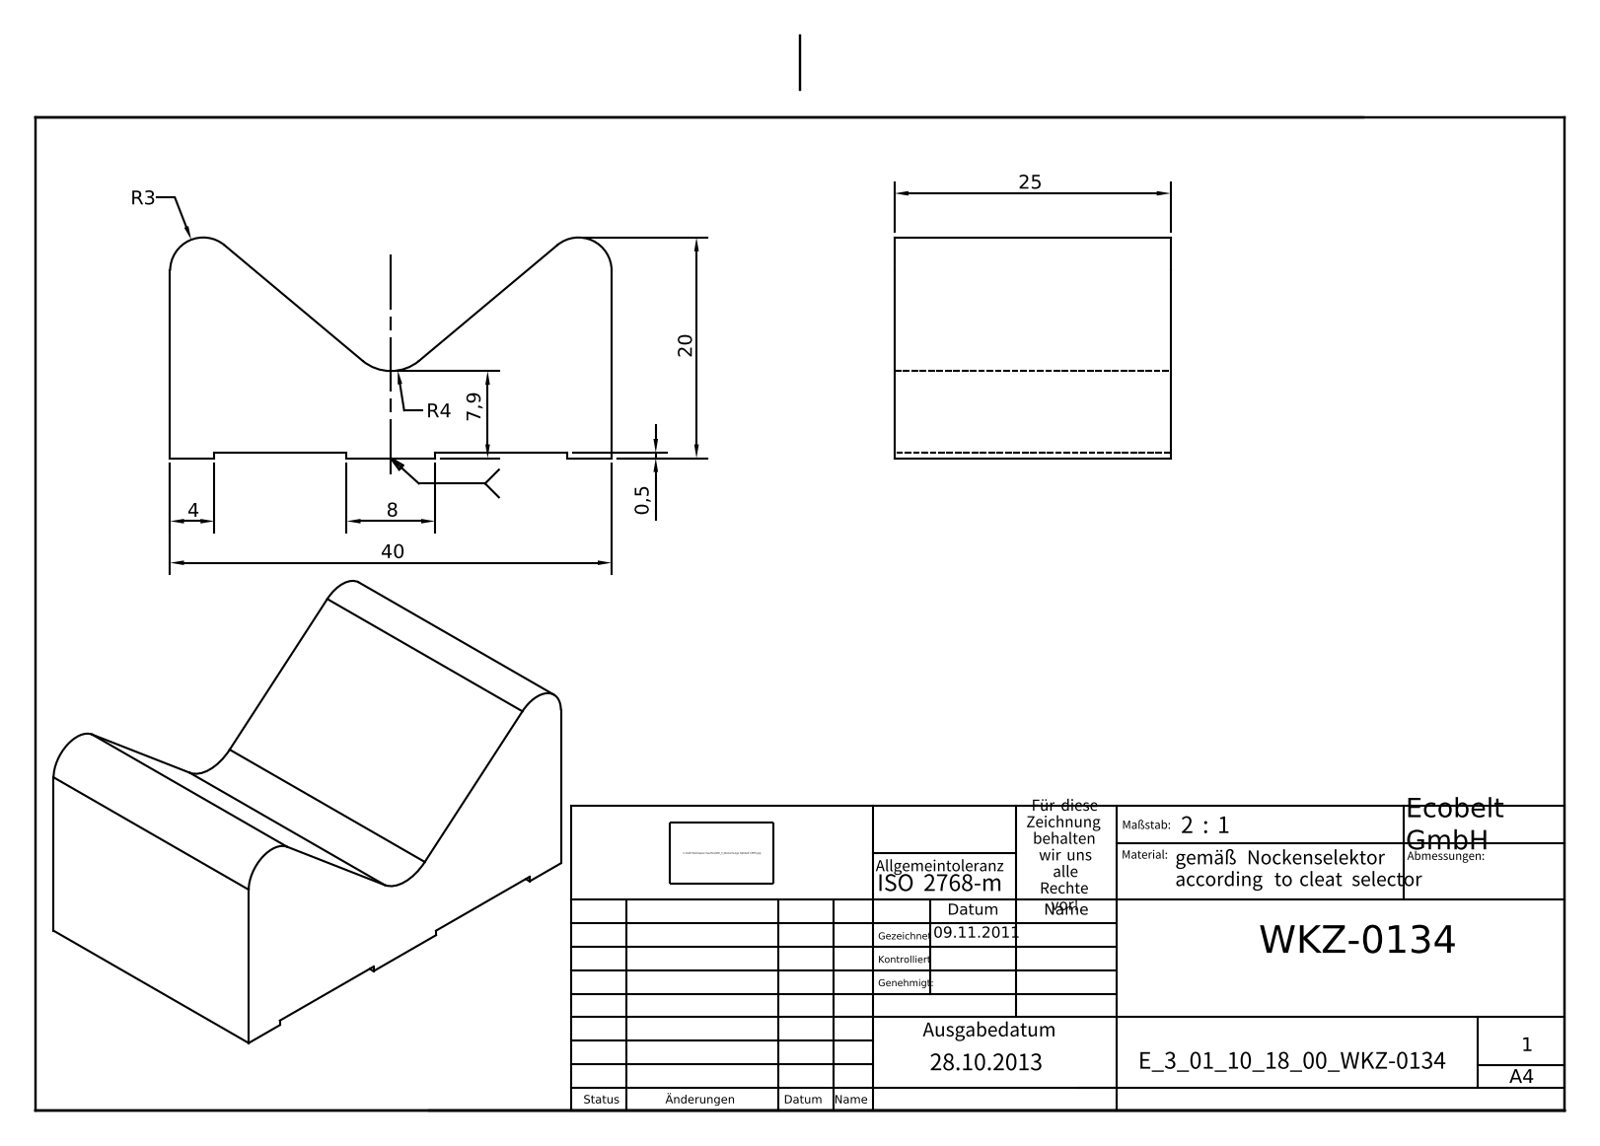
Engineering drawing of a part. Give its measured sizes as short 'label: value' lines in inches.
name: E_3_01_10_18_00_WKZ-0134
written by: Autodesk Inventor 2025 (AUTOMOTIVE_DESIGN)
unit: in
bodies: 1 solid, 18 faces (15 planar, 3 cylindrical, 0 other)
size: 1.575 × 0.984 × 0.787
volume: 0.876 in³; area: 6.733 in²
rounds: 2× R0.118, 1× R0.157
face distances: 0.984, 1.575, 0.02, 0.157, 0.63, 0.945, 1.417, 0.472, 0.787, 1.26
